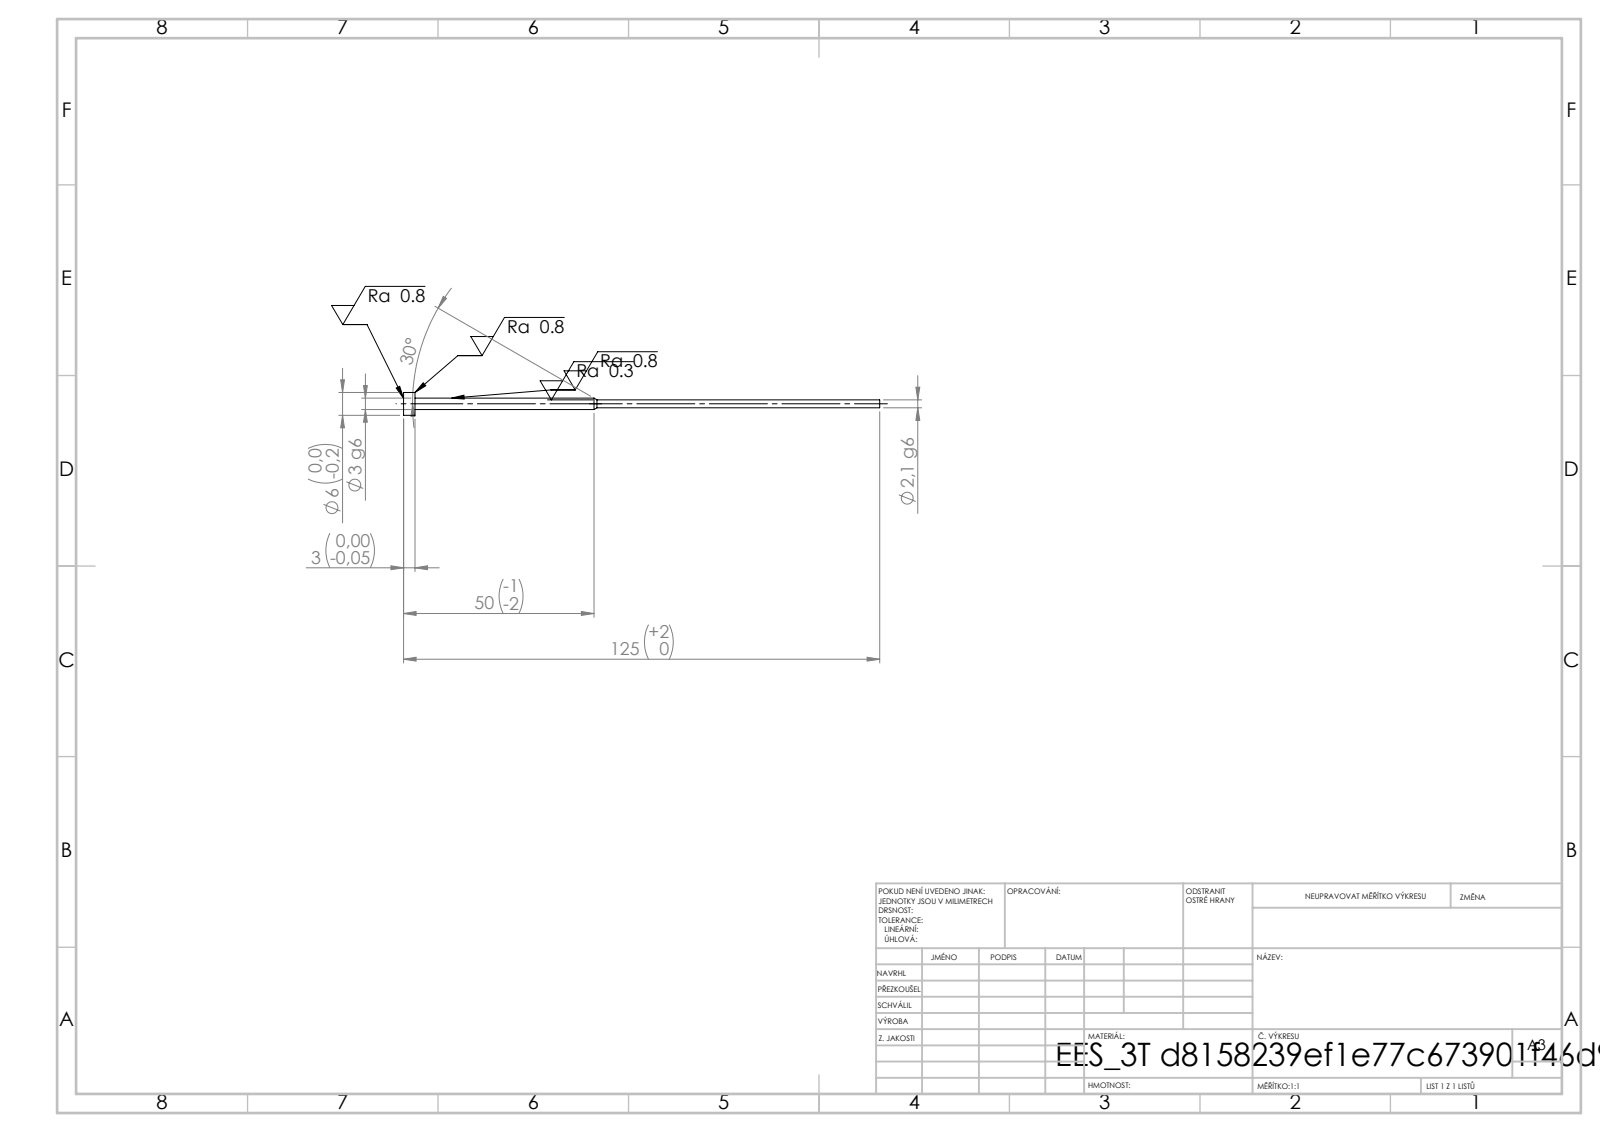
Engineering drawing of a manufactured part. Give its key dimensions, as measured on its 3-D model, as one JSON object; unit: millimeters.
{"step_written_by": "SolidWorks 2019 (CONFIG_CONTROL_DESIGN)", "units": "millimeters", "bodies": {"solids": 1, "faces": 11, "planar": 3, "cylindrical": 6, "other": 2}, "overall_size": [125, 6, 6], "volume_mm3": 678, "surface_area_mm2": 1049, "round_bosses_or_shafts": [[6, 1], [3, 1], [2.1, 1]], "face_to_face_distances": [3, 122, 125]}
